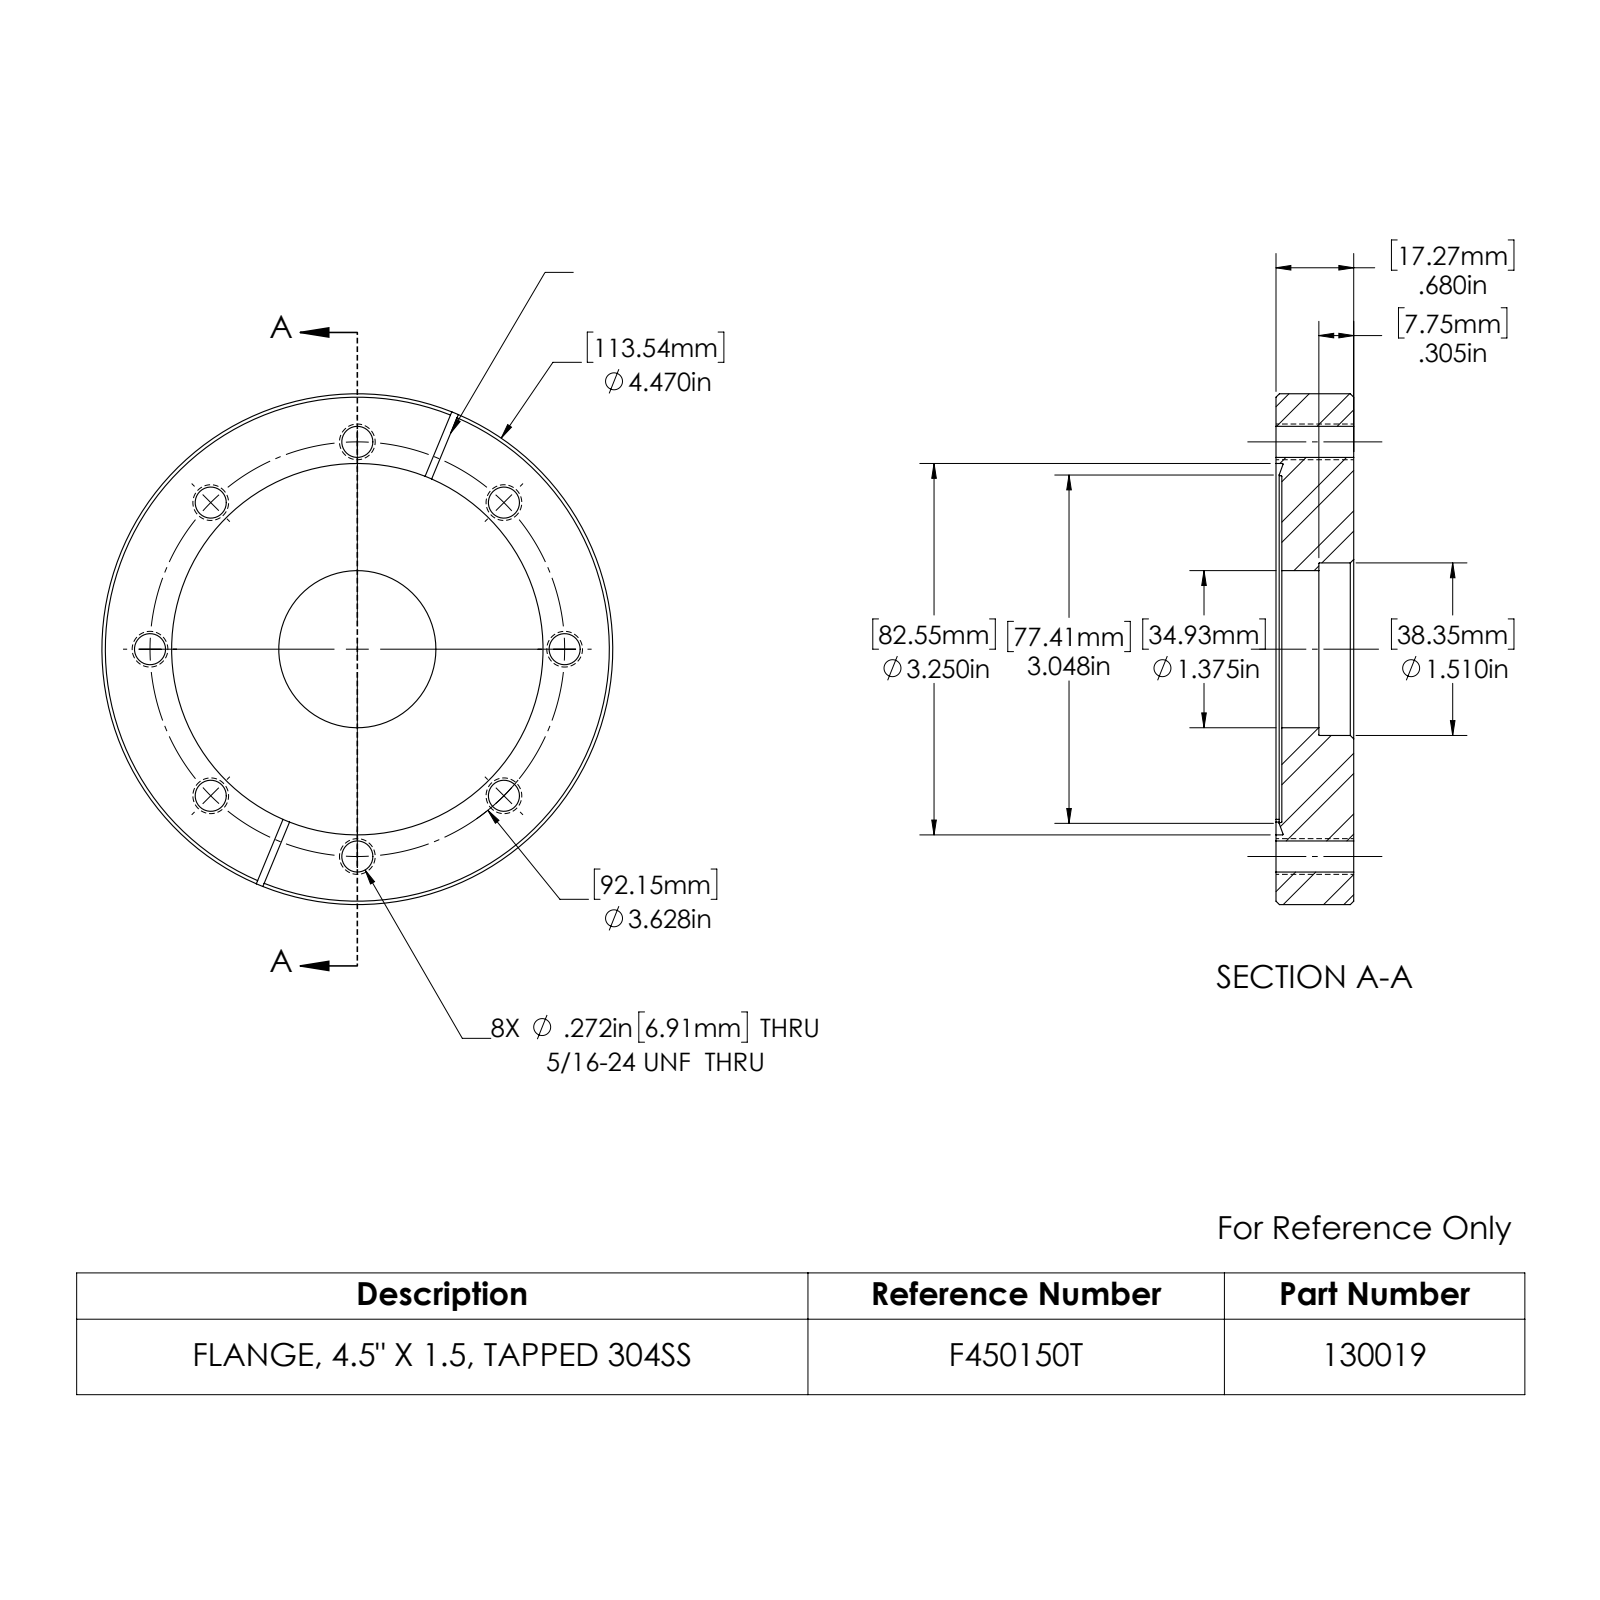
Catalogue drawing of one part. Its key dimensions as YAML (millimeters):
part_name: "130019_D"
step_written_by: "SolidWorks 2022 (CONFIG_CONTROL_DESIGN)"
units: millimeters
bodies: {solids: 1, faces: 54, planar: 11, cylindrical: 24, other: 19}
overall_size: [113.5, 113.5, 17.3]
volume: 145700
surface_area: 28960
round_holes:
  - {diameter: 6.9, count: 8}
  - {diameter: 34.9, count: 1}
  - {diameter: 38.4, count: 1}
  - {diameter: 82.6, count: 1}
round_bosses_or_shafts:
  - {diameter: 113.5, count: 1}
face_to_face_distances: [17.3, 1.3, 16, 9.5, 8.2, 7.7, 1.3, 8.2, 16, 1.6]
hole_center_spacings: [35.3, 46.1, 85.1, 65.2, 65.2, 92.2, 92.2]
